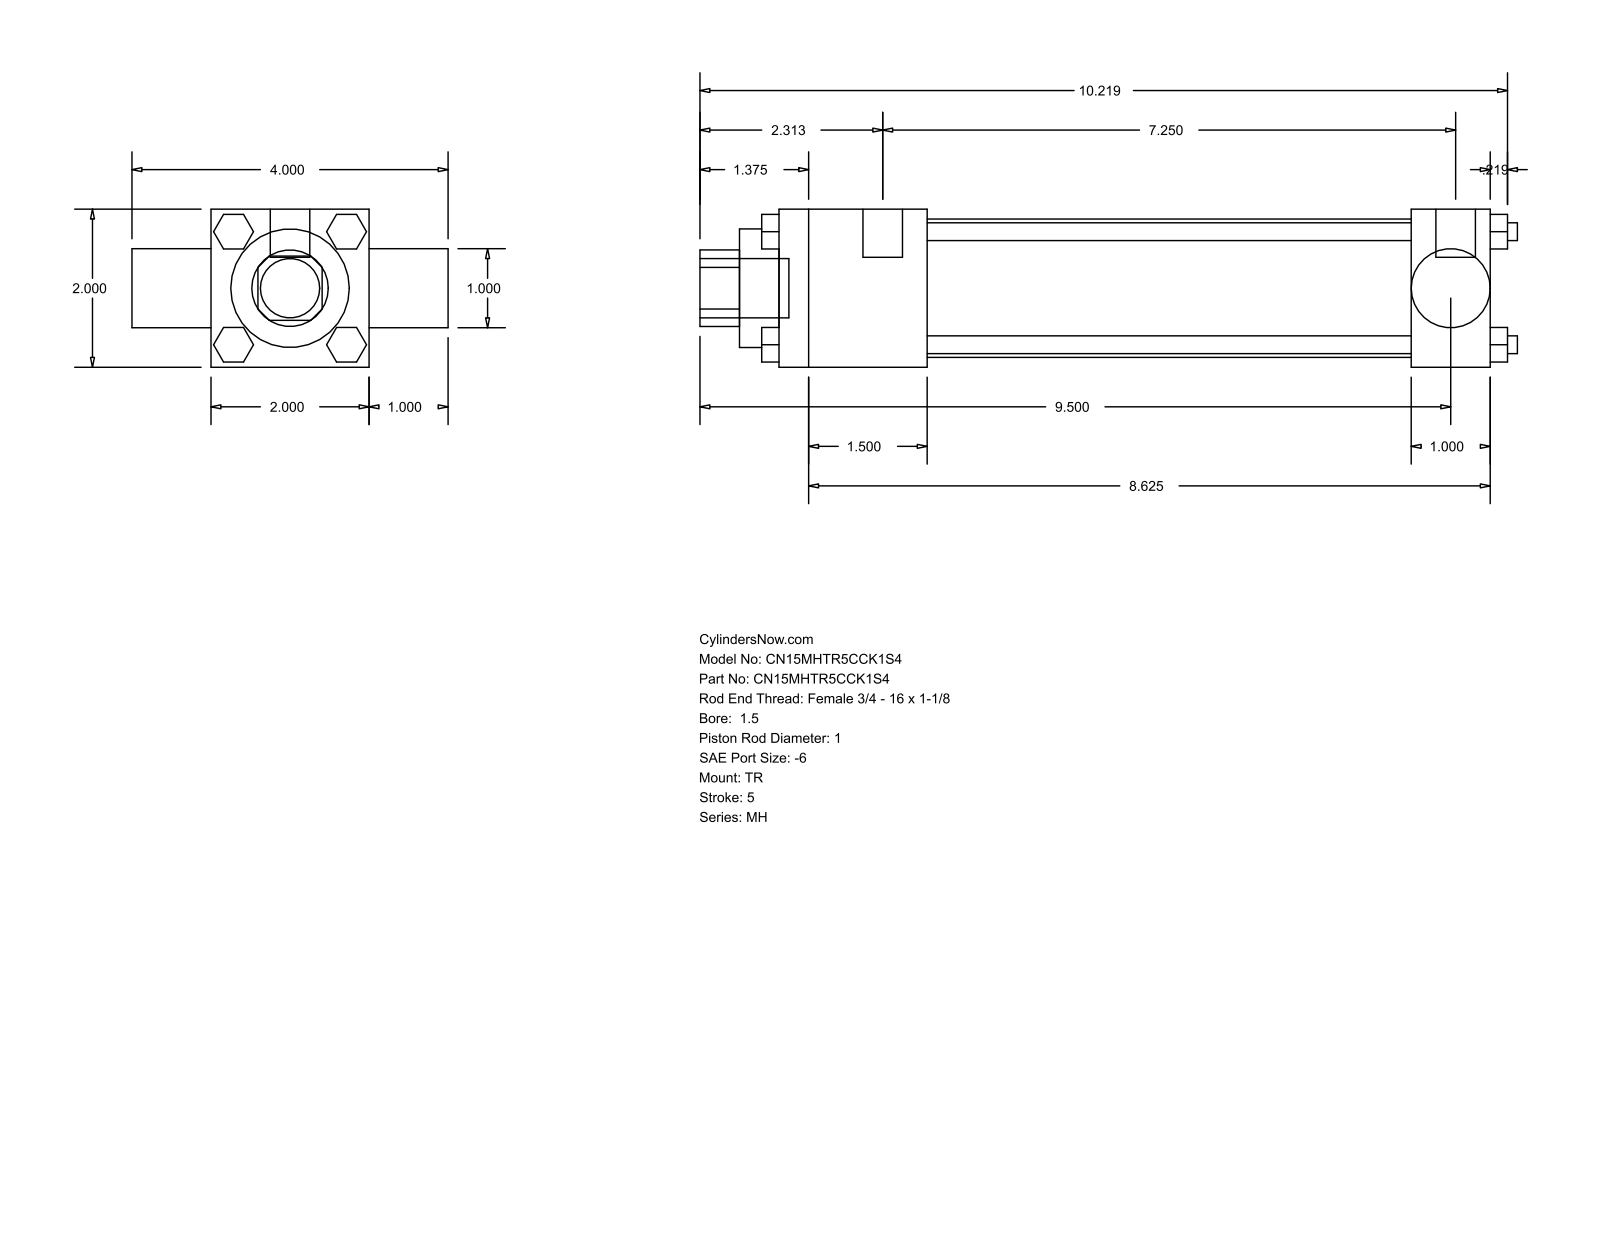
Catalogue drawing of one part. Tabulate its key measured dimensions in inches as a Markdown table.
| quantity | value |
| --- | --- |
| part name | MH_TR__0150_1 |
| STEP written by | GSSL Pune (CONFIG_CONTROL_DESIGN) |
| units | inches |
| bodies | 0 solids, 120 faces (92 planar, 28 cylindrical, 0 other) |
| overall size | 10.344 × 4 × 2 |
| round holes (diameter × count) | 0.998 × 1, 1 × 1, 1.5 × 1, 1.75 × 1 |
| round bosses / shafts (diameter × count) | 0.225 × 4, 0.219 × 3, 0.5 × 2, 0.75 × 1 |
| partial cylindrical surfaces (radius × count) | 0.484 × 1 |
| main face-to-face distances | 2, 1, 9, 3, 1.875, 7.125, 8, 6.125, 9.219, 0.5 |
